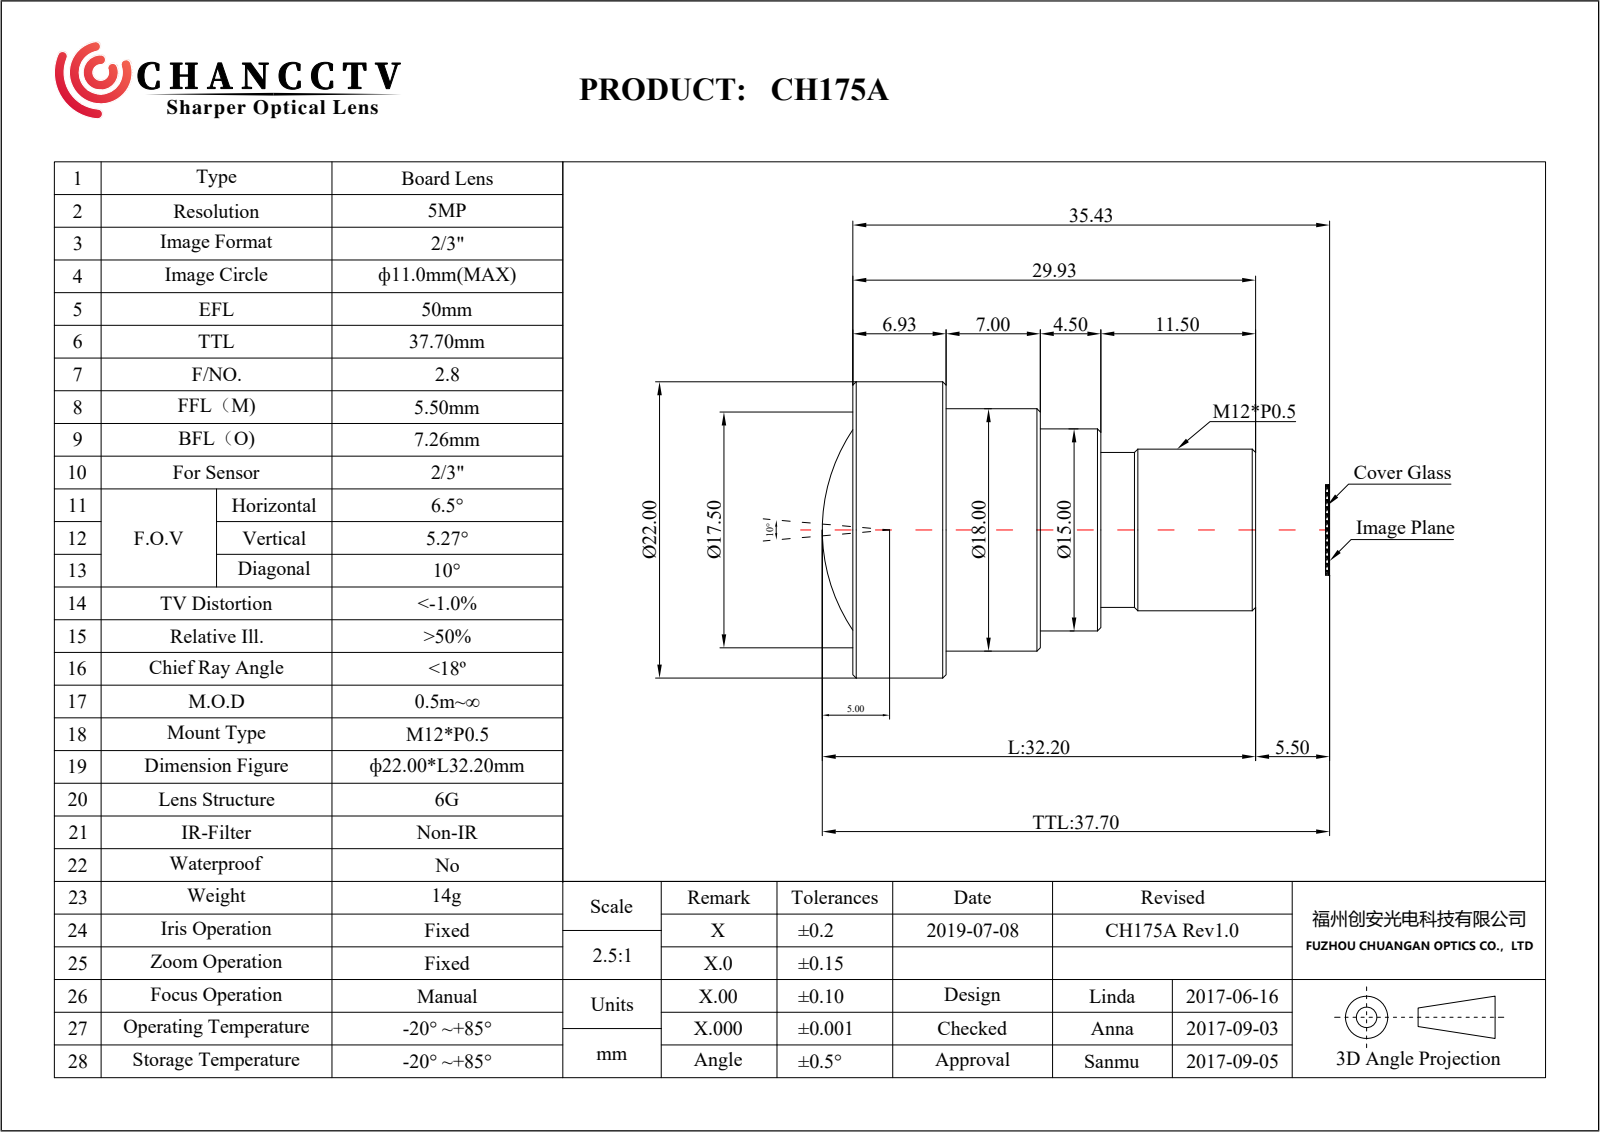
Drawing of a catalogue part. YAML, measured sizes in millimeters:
part_name: "PRT0001"
step_written_by: "CREO PARAMETRIC BY PTC INC, 2019010 (CONFIG_CONTROL_DESIGN)"
units: millimeters
bodies: {solids: 1, faces: 80, planar: 6, cylindrical: 45, other: 29}
overall_size: [32.2, 22, 22]
volume: 6335
surface_area: 2662
round_holes:
  - {diameter: 9.2, count: 1}
  - {diameter: 11, count: 1}
round_bosses_or_shafts:
  - {diameter: 22, count: 1}
  - {diameter: 18, count: 1}
  - {diameter: 15, count: 1}
  - {diameter: 12, count: 1}
face_to_face_distances: [7, 11.5, 18.5, 14, 4.5, 27.73, 20.73, 13.73, 9.23, 29.93]
